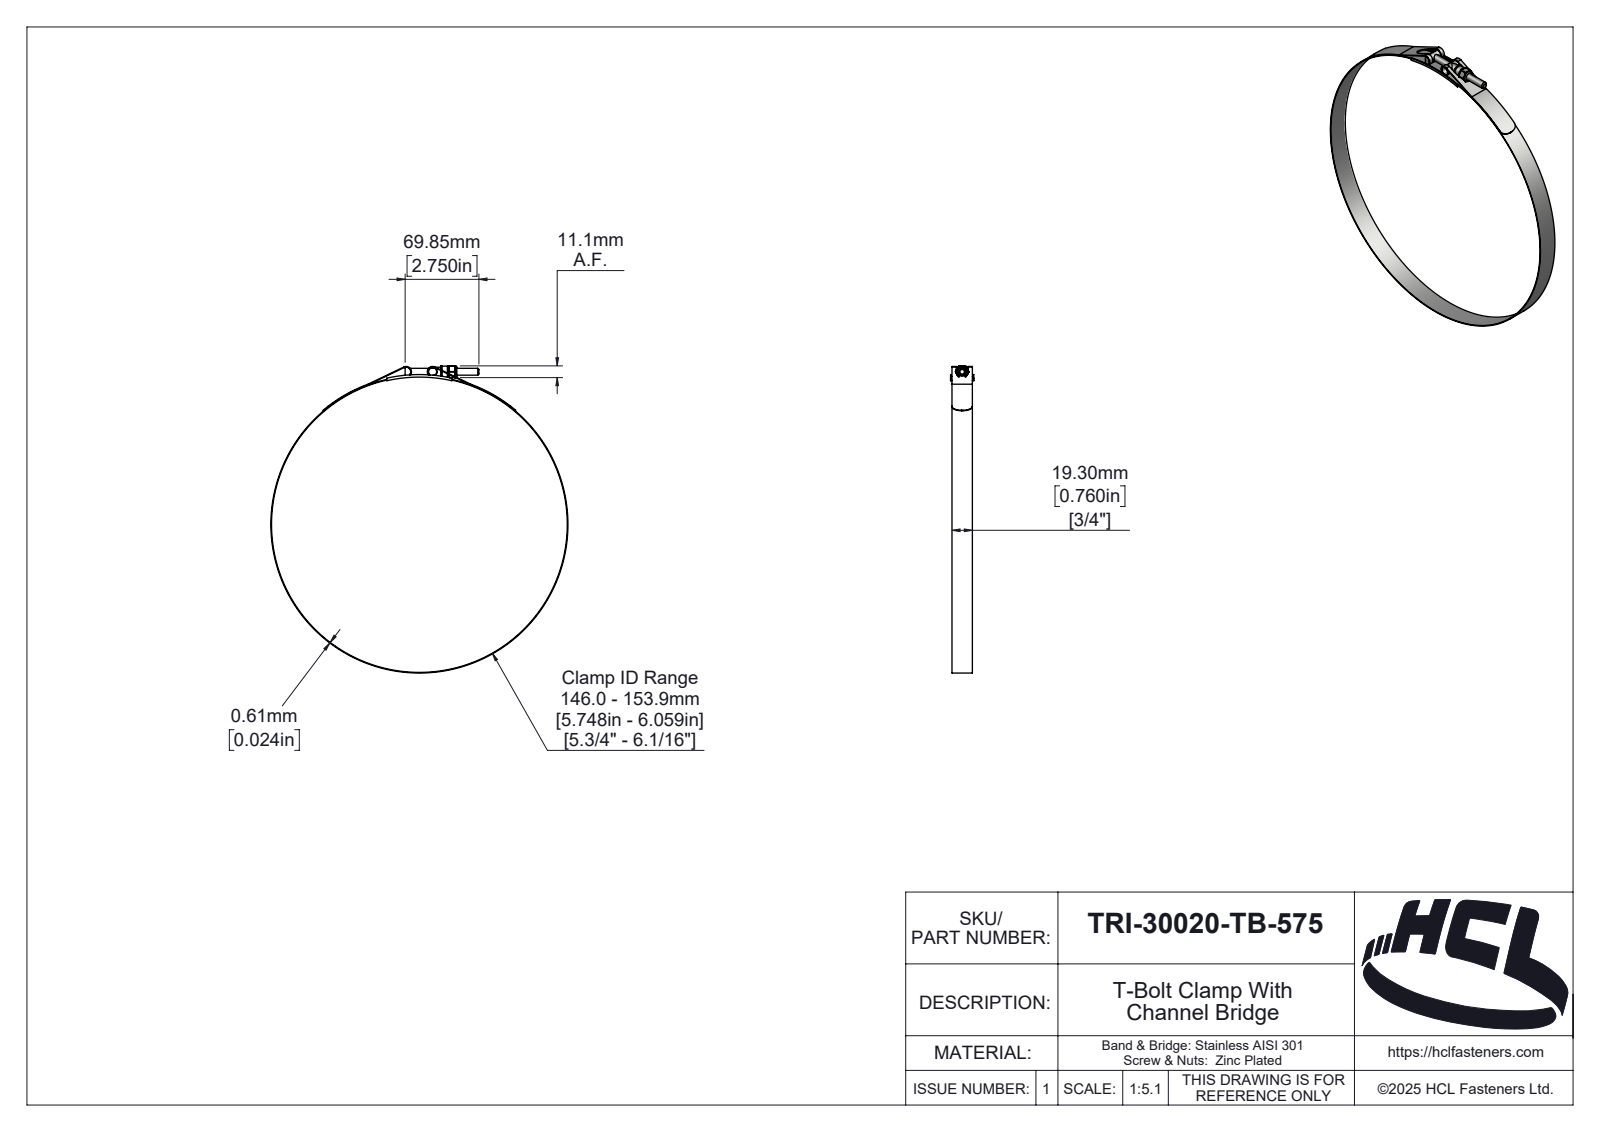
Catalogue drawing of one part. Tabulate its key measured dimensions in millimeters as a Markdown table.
| quantity | value |
| --- | --- |
| part name | TRI-30020-TB-575 |
| STEP written by | SolidWorks 2025 (AUTOMOTIVE_DESIGN) |
| units | millimeters |
| bodies | 6 solids, 330 faces (44 planar, 122 cylindrical, 164 other) |
| overall size | 290.79 × 281.22 × 22 |
| volume | 17 227 mm³ |
| surface area | 48 622 mm² |
| round holes (diameter × count) | 5.4 × 1, 6.35 × 1, 6.5 × 1, 7.58 × 1, 280 × 1 |
| round bosses / shafts (diameter × count) | 8.58 × 2, 281.22 × 1, 10.58 × 1 |
| partial cylindrical surfaces (radius × count) | 0.39 × 6, 0.5 × 2, 4.39 × 2, 5 × 2, 0.59 × 1, 2.42 × 1, 3.03 × 1, 3.19 × 1 |
| main face-to-face distances | 0.61, 19.3, 1.35, 20.65, 0.74, 21.39, 20.04, 22, 20.78, 11.12 |
| hole center spacings | 145 |
